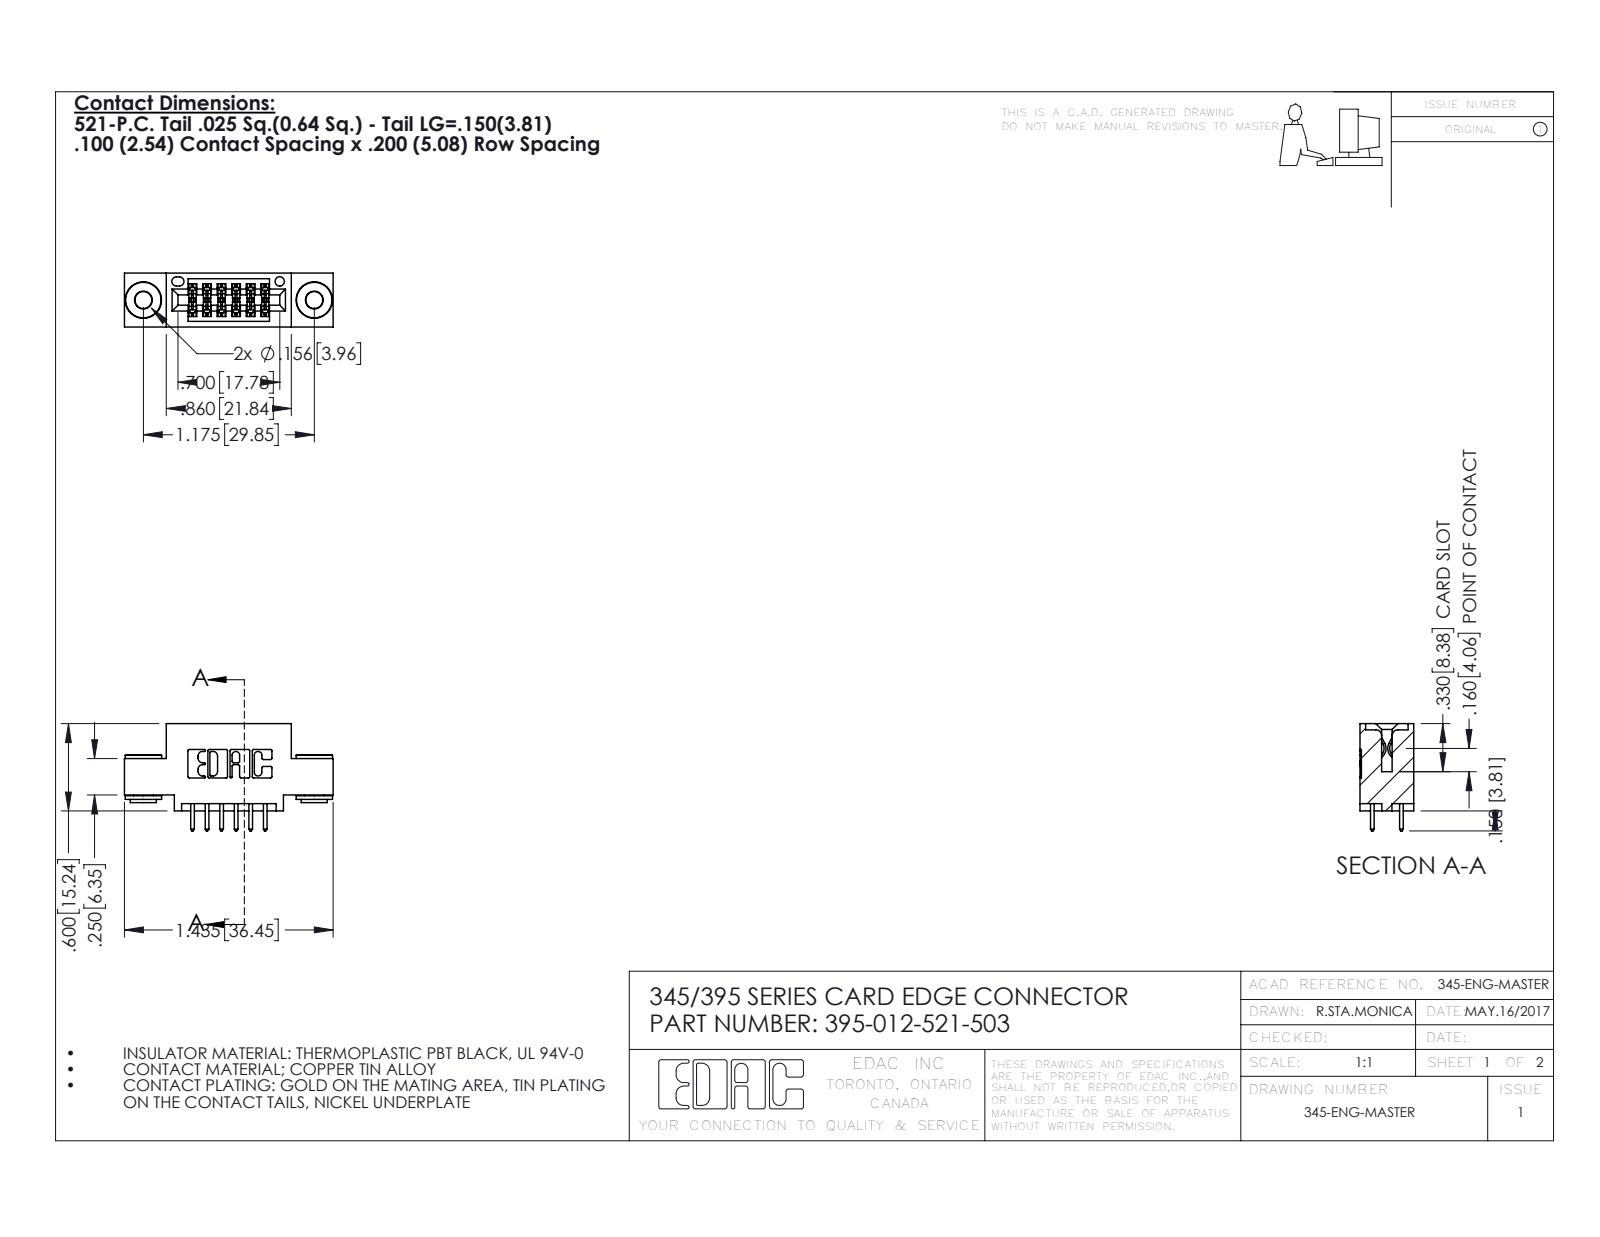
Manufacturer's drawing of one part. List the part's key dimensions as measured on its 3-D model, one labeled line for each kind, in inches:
Part name (STEP PRODUCT): 345-250-002_345-250-002-102; 345 Part_0.110 Offset - 0.156 Dia-TH; 395-012-521-503; 345-292-001_345-293-121
STEP written by: SolidWorks 2016 (CONFIG_CONTROL_DESIGN)
Units: inches
Bodies: 15 solids, 768 faces (490 planar, 270 cylindrical, 8 other)
Overall size (bounding box): 1.435 × 0.737 × 0.37
Volume: 0.192 in³ · Surface area: 6.543 in²
Round holes (diameter × count): ⌀0.116 ×2, ⌀0.156 ×2, ⌀0.064 ×1
Round bosses / shafts (diameter × count): ⌀0.25 ×2, ⌀0.18 ×2, ⌀0.136 ×2
Partial cylindrical surfaces — rounded edges, fillets, slot ends (radius × count): R0.01 ×22, R0.006 ×18, R0.01 ×12, R0.007 ×6, R0.031 ×6, R0.026 ×3, R0.014 ×2, R0.019 ×2
Main face-to-face distances: 0.2, 0.072, 0.298, 0.37, 0.025, 0.1, 0.098, 0.272, 0.25, 0.225
Hole centre spacings: 0.27, 0.946, 1.175
